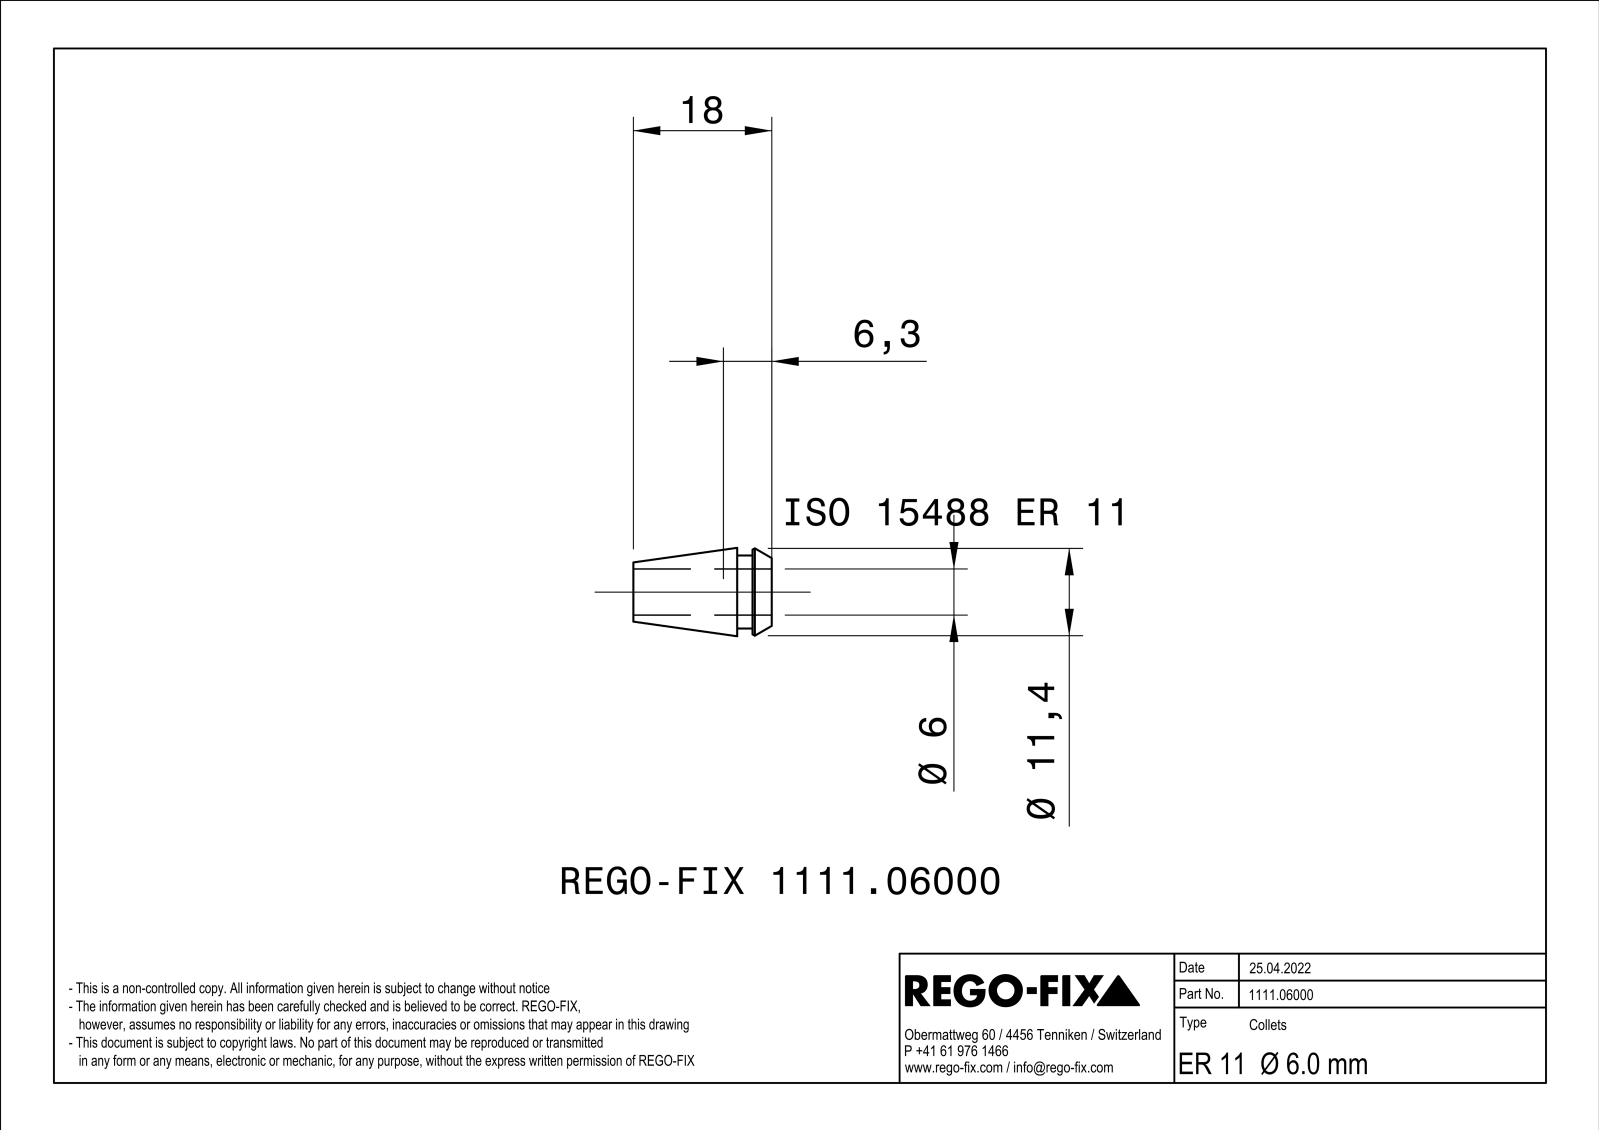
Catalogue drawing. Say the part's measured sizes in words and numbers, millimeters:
The part is named "NOCUT". Its 3-D file was written by "SIEMENS PLM Software Solid Edge ST10 (AUTOMOTIVE_DESIGN)". It is 1 solid with 157 faces: 66 planar, 37 cylindrical and 54 other. Overall it measures 18 by 11.5 by 11.49 millimeters. Its volume is 684 cubic millimeters and its surface area 1 500 square millimeters. Round holes: 1 of diameter 6. Round bosses or shafts: 1 of diameter 11.5, 1 of diameter 9.5. Partial cylindrical surfaces (rounded edges, fillets, slot ends): 12 of radius 25. The main face-to-face distances are 0.45, 0.46, 0.44, 2, 2.5, 4.5, 18, 15.5, 13.5, 4.
